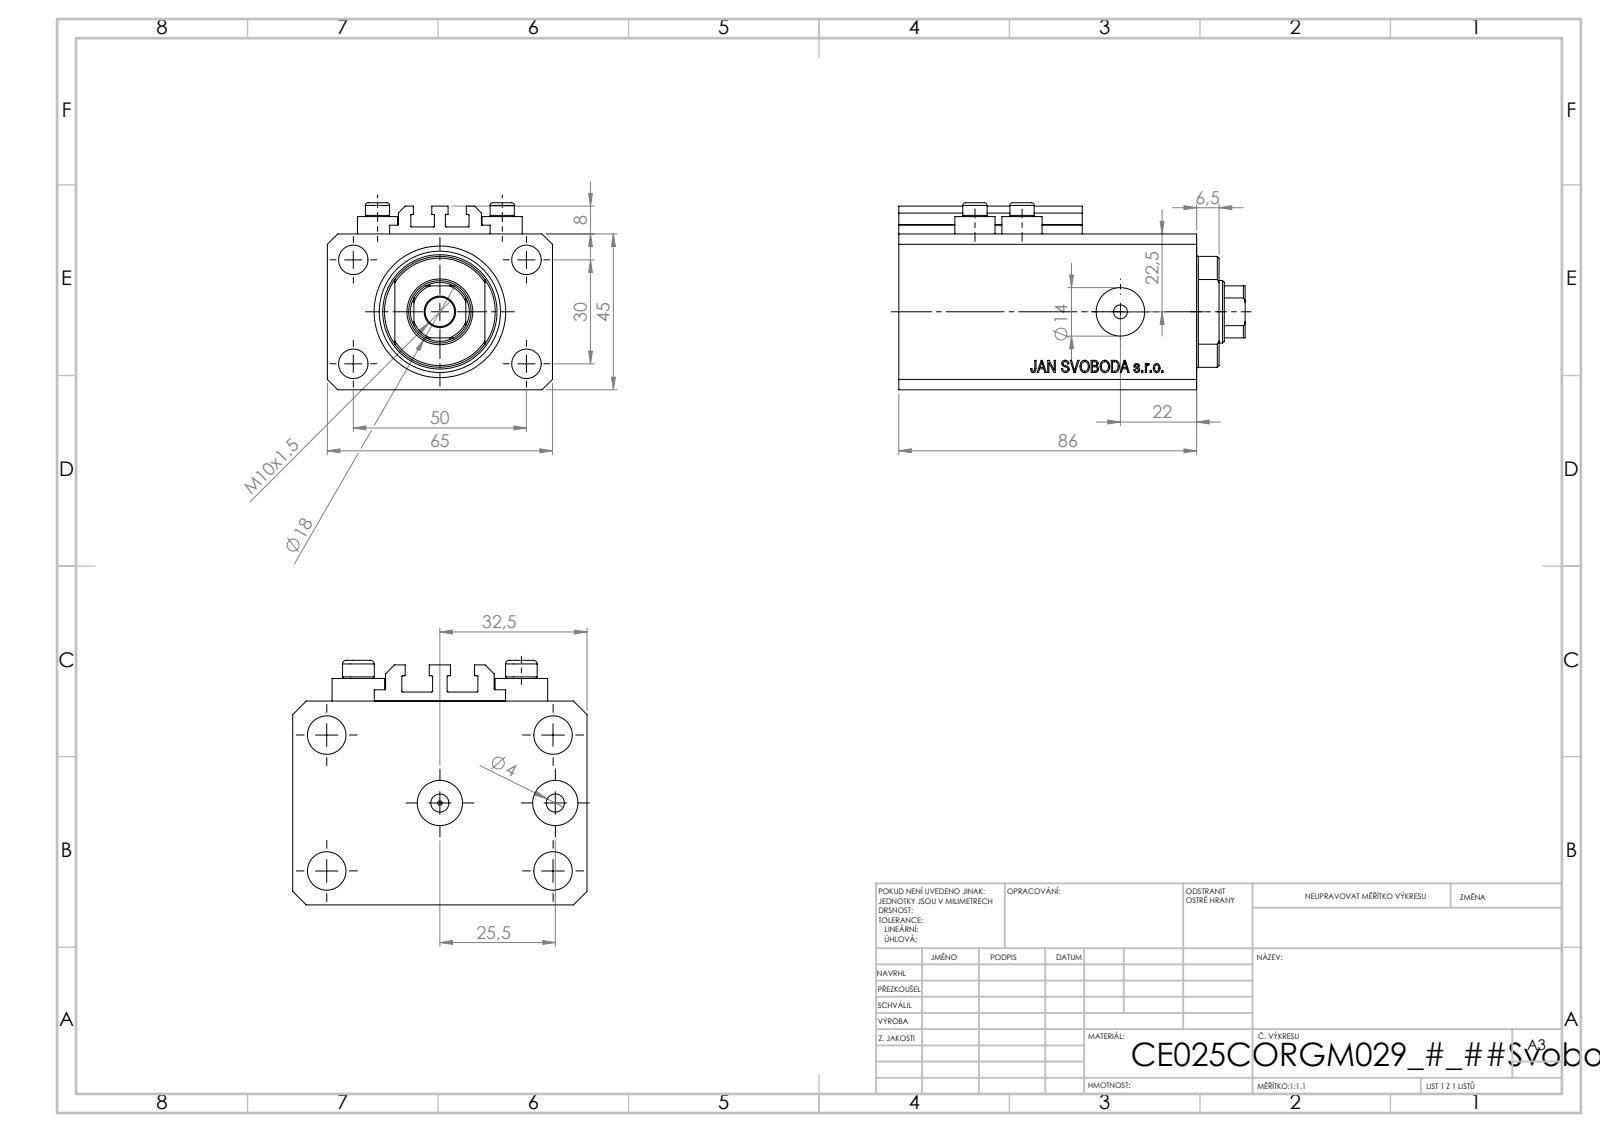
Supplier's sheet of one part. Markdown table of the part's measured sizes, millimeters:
| quantity | value |
| --- | --- |
| part name | ALLEN BOLT V250CE; V250CE_VC_C; V250CE_C_VCP; V250CE_C_Body |
| STEP written by | SolidWorks 2019 (CONFIG_CONTROL_DESIGN) |
| units | millimeters |
| bodies | 8 solids, 1042 faces (504 planar, 92 cylindrical, 446 other) |
| overall size | 100 × 65 × 54 |
| volume | 234 629 mm³ |
| surface area | 62 681 mm² |
| round holes (diameter × count) | 4 × 8, 8.5 × 5, 10 × 2, 14 × 2, 1.25 × 1, 18 × 1, 25 × 1, 38 × 1 |
| round bosses / shafts (diameter × count) | 11.6 × 4, 7 × 4 |
| partial cylindrical surfaces (radius × count) | 0.2 × 10, 8.5 × 1, 16 × 1 |
| main face-to-face distances | 45, 65, 14, 86, 72, 47, 65.1, 6.9, 79.1, 3 |
| hole center spacings | 29.15, 13.6, 15.01, 30, 36, 38.48, 50, 52.68 |
